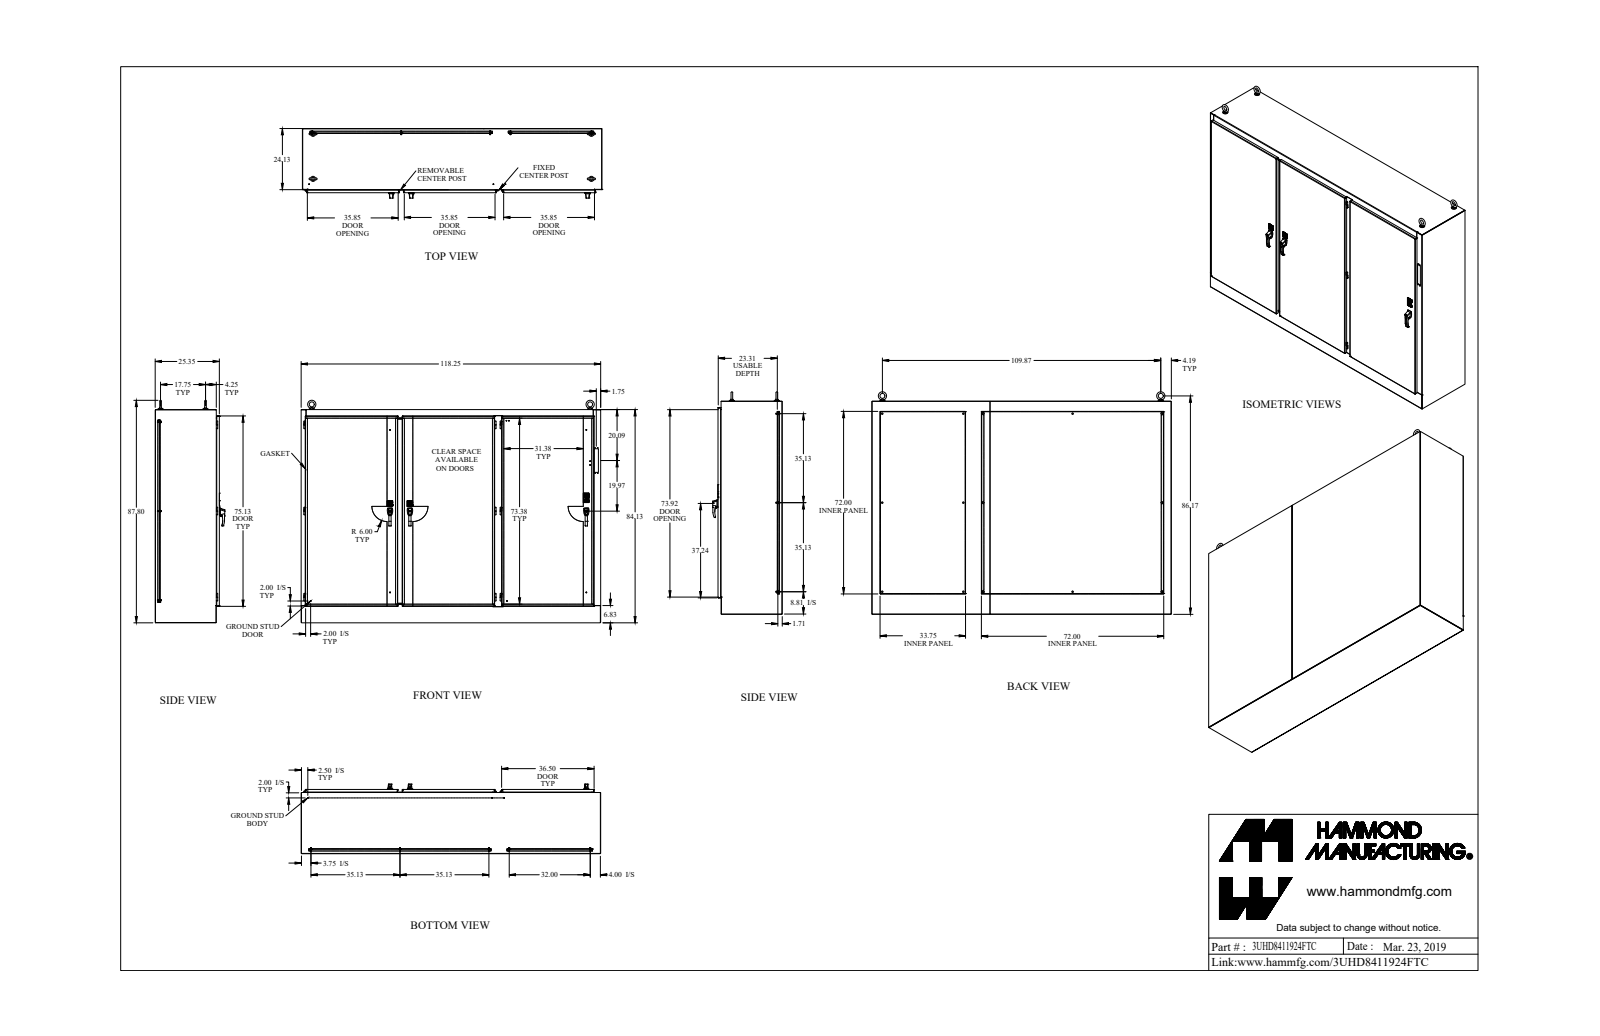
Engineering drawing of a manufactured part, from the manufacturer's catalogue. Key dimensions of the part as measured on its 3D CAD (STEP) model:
Part name (STEP PRODUCT): 3UHD8411924FTC
STEP written by: SolidWorks 2018 (AUTOMOTIVE_DESIGN)
Units: inches
Bodies: 310 solids, 4344 faces (2654 planar, 1217 cylindrical, 473 other)
Overall size (bounding box): 118.25 × 87.799 × 27.464
Volume: 4 856 in³ · Surface area: 90 472 in²
Round holes (diameter × count): ⌀0.25 ×20, ⌀0.196 ×19, ⌀0.307 ×17, ⌀0.281 ×12, ⌀0.445 ×11, ⌀0.313 ×9, ⌀0.35 ×9, ⌀0.875 ×8, ⌀0.266 ×6, ⌀0.39 ×6, ⌀0.257 ×4, ⌀0.28 ×4
Round bosses / shafts (diameter × count): ⌀1 ×18, ⌀0.25 ×18, ⌀0.375 ×15, ⌀0.65 ×14, ⌀0.33 ×14, ⌀0.281 ×12, ⌀0.246 ×10, ⌀0.486 ×7
Partial cylindrical surfaces — rounded edges, fillets, slot ends (radius × count): R0.06 ×75, R0.125 ×62, R0.185 ×54, R0.017 ×48, R0.5 ×45, R0.03 ×18, R0.09 ×18, R0.13 ×16
Main face-to-face distances: 0.125, 0.079, 23.431, 25.369, 25.243, 25.29, 25.165, 1.937, 1.812, 23.353
Hole centre spacings: 70.25, 35.125, 35.125, 2.126, 7.87, 17.75, 69.629, 77.499
